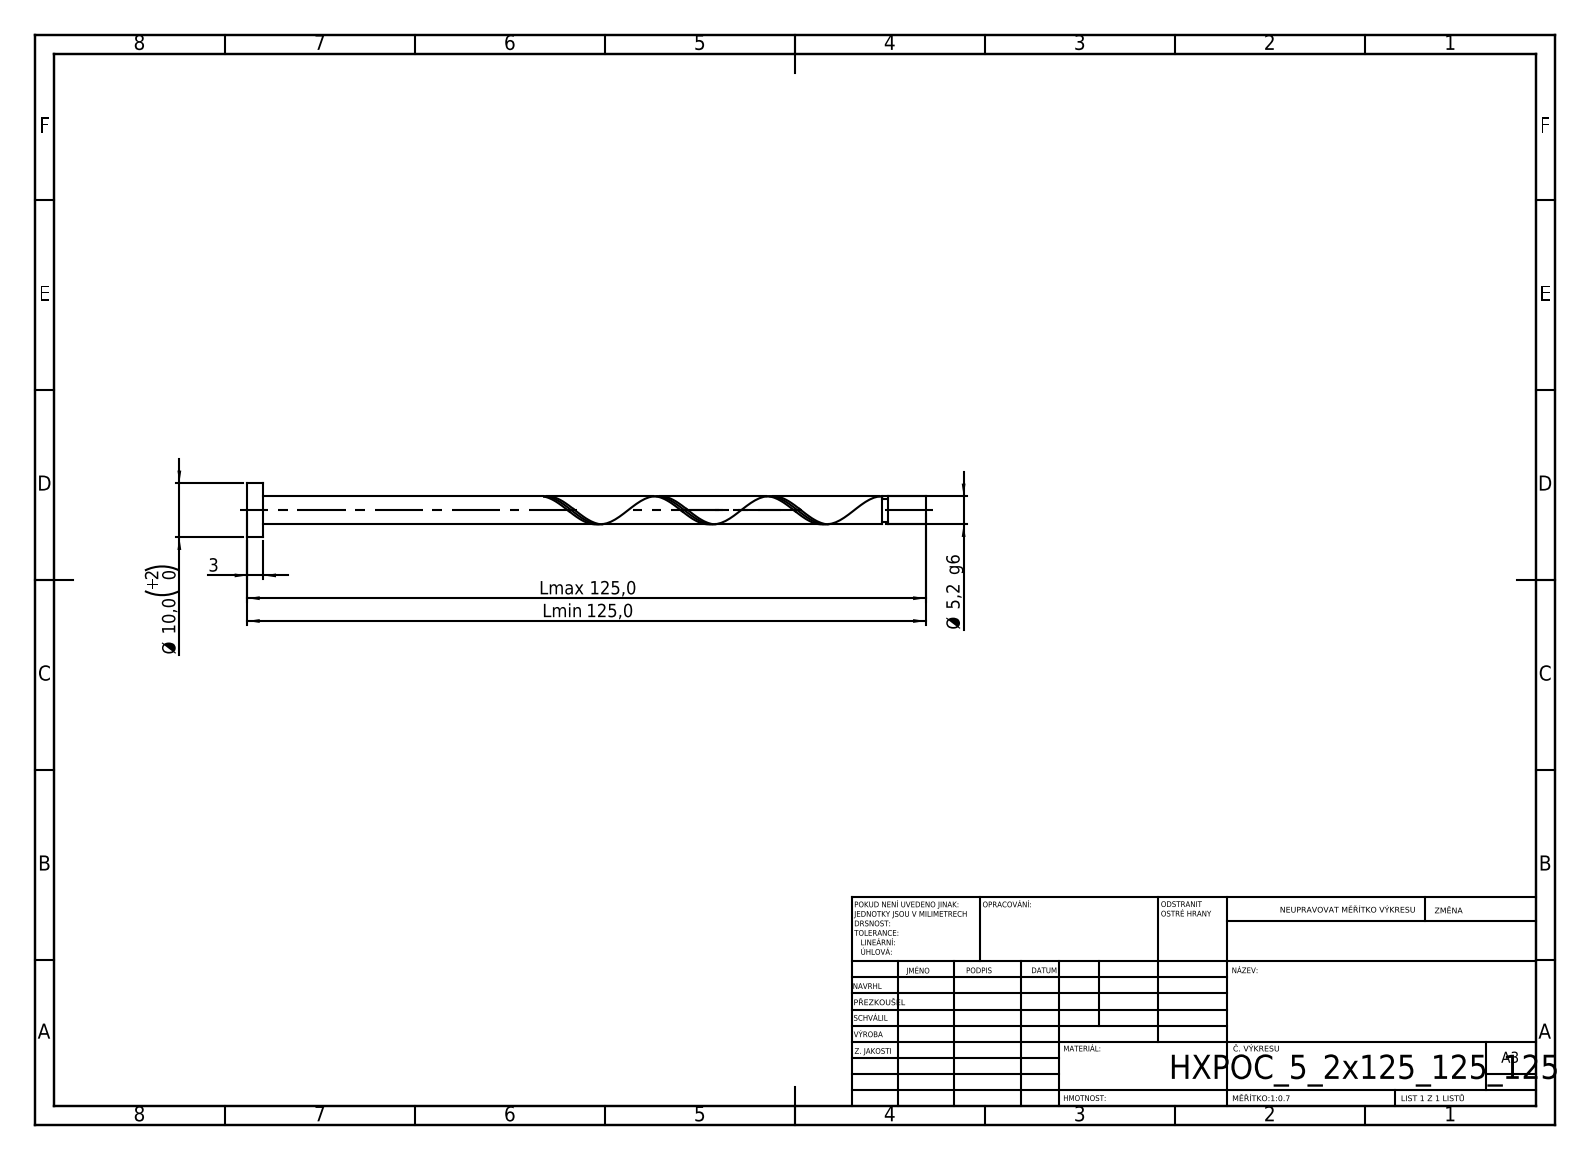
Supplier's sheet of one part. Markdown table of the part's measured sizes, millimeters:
| quantity | value |
| --- | --- |
| STEP written by | SolidWorks 2019 (CONFIG_CONTROL_DESIGN) |
| units | millimeters |
| bodies | 1 solid, 21 faces (6 planar, 14 cylindrical, 1 other) |
| overall size | 125 × 10 × 10 |
| volume | 2 793 mm³ |
| surface area | 2 299 mm² |
| round bosses / shafts (diameter × count) | 10 × 1, 5.2 × 1, 4.16 × 1 |
| main face-to-face distances | 3, 125, 122, 118.07, 115.07, 6.93, 117.03, 114.03, 1.04, 7.97 |
